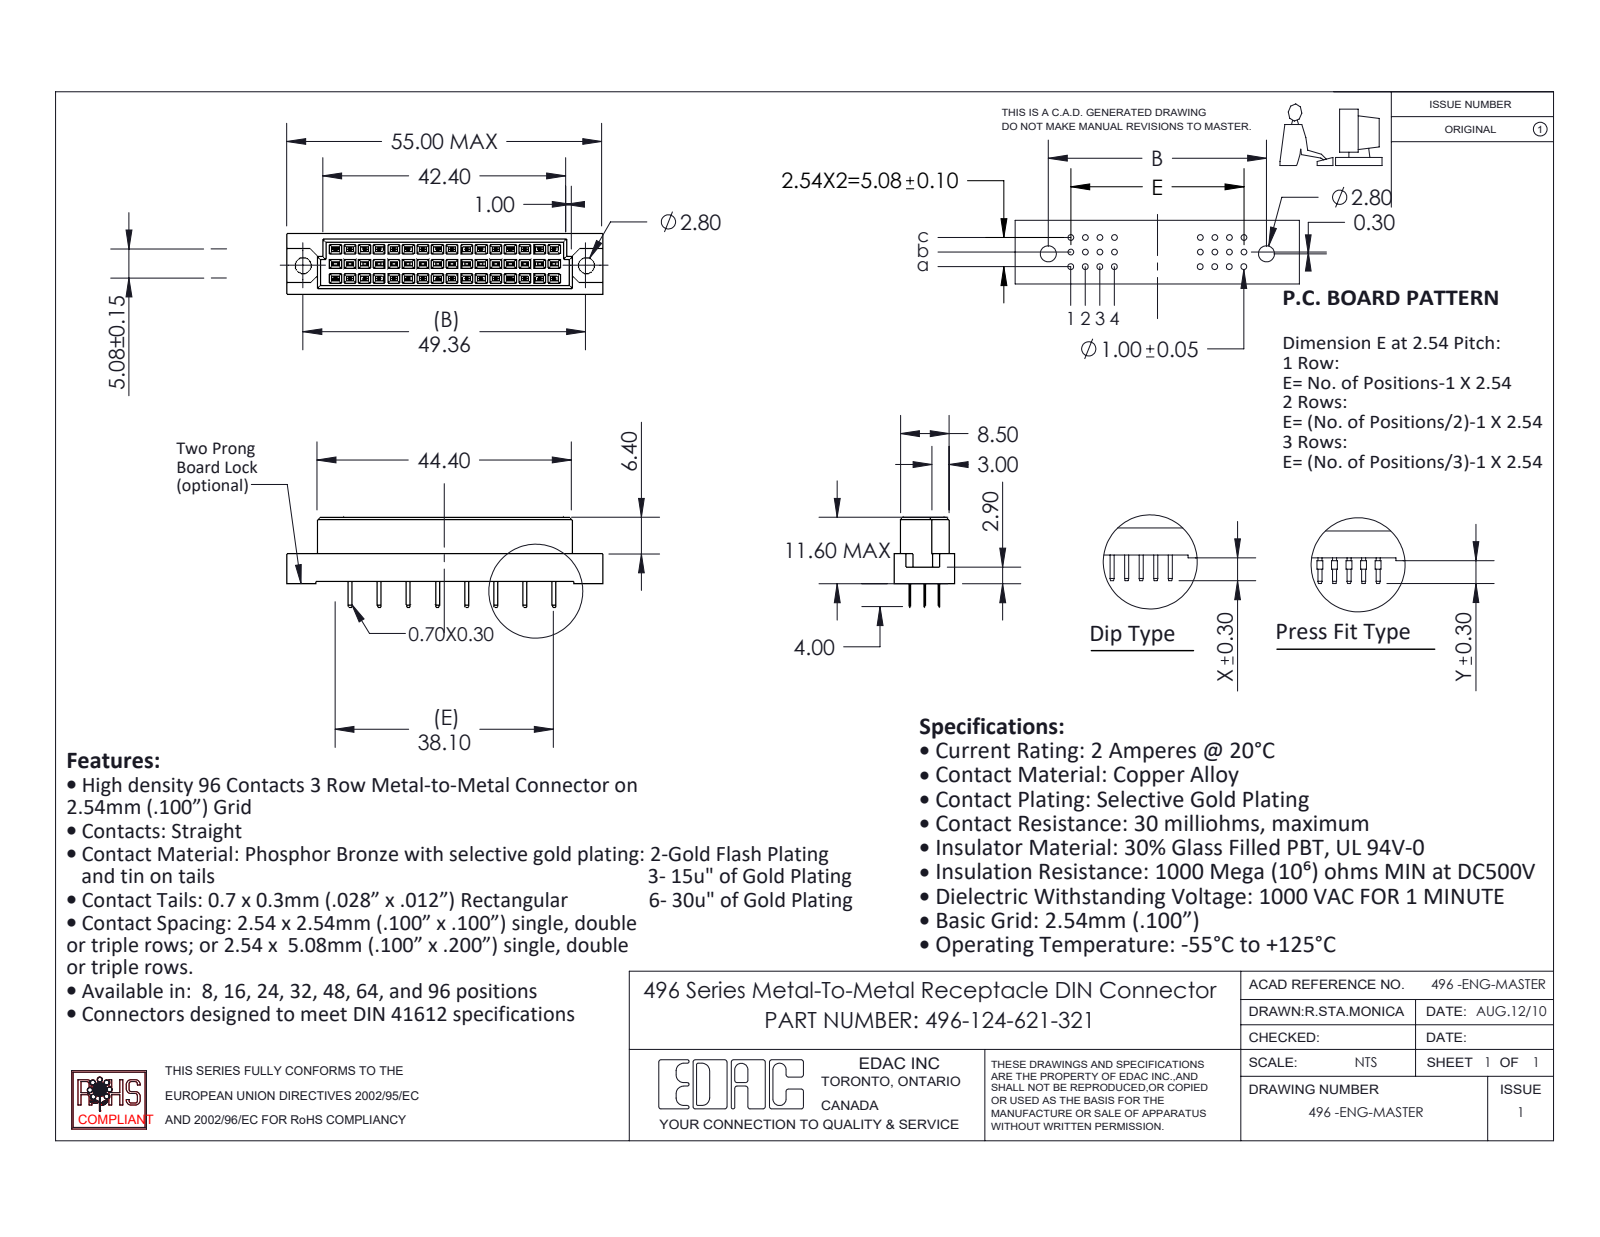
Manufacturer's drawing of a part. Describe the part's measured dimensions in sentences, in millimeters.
The part is named "496-290_21; 496 Part_48; 496-124-621-321". Its 3-D file was written by "SolidWorks 2020 (CONFIG_CONTROL_DESIGN)". It is 25 solids with 906 faces: 902 planar, 4 cylindrical and 0 other. Overall it measures 55 by 15.6 by 10.6 millimeters. Its volume is 4 631 cubic millimeters and its surface area 4 618 square millimeters. Round holes: 2 of diameter 2.8. The main face-to-face distances are 2.54, 5.08, 1.05, 9.55, 0.81, 0.56, 0.55, 10.6, 3.35, 1.73. The hole center spacings are 49.36.
